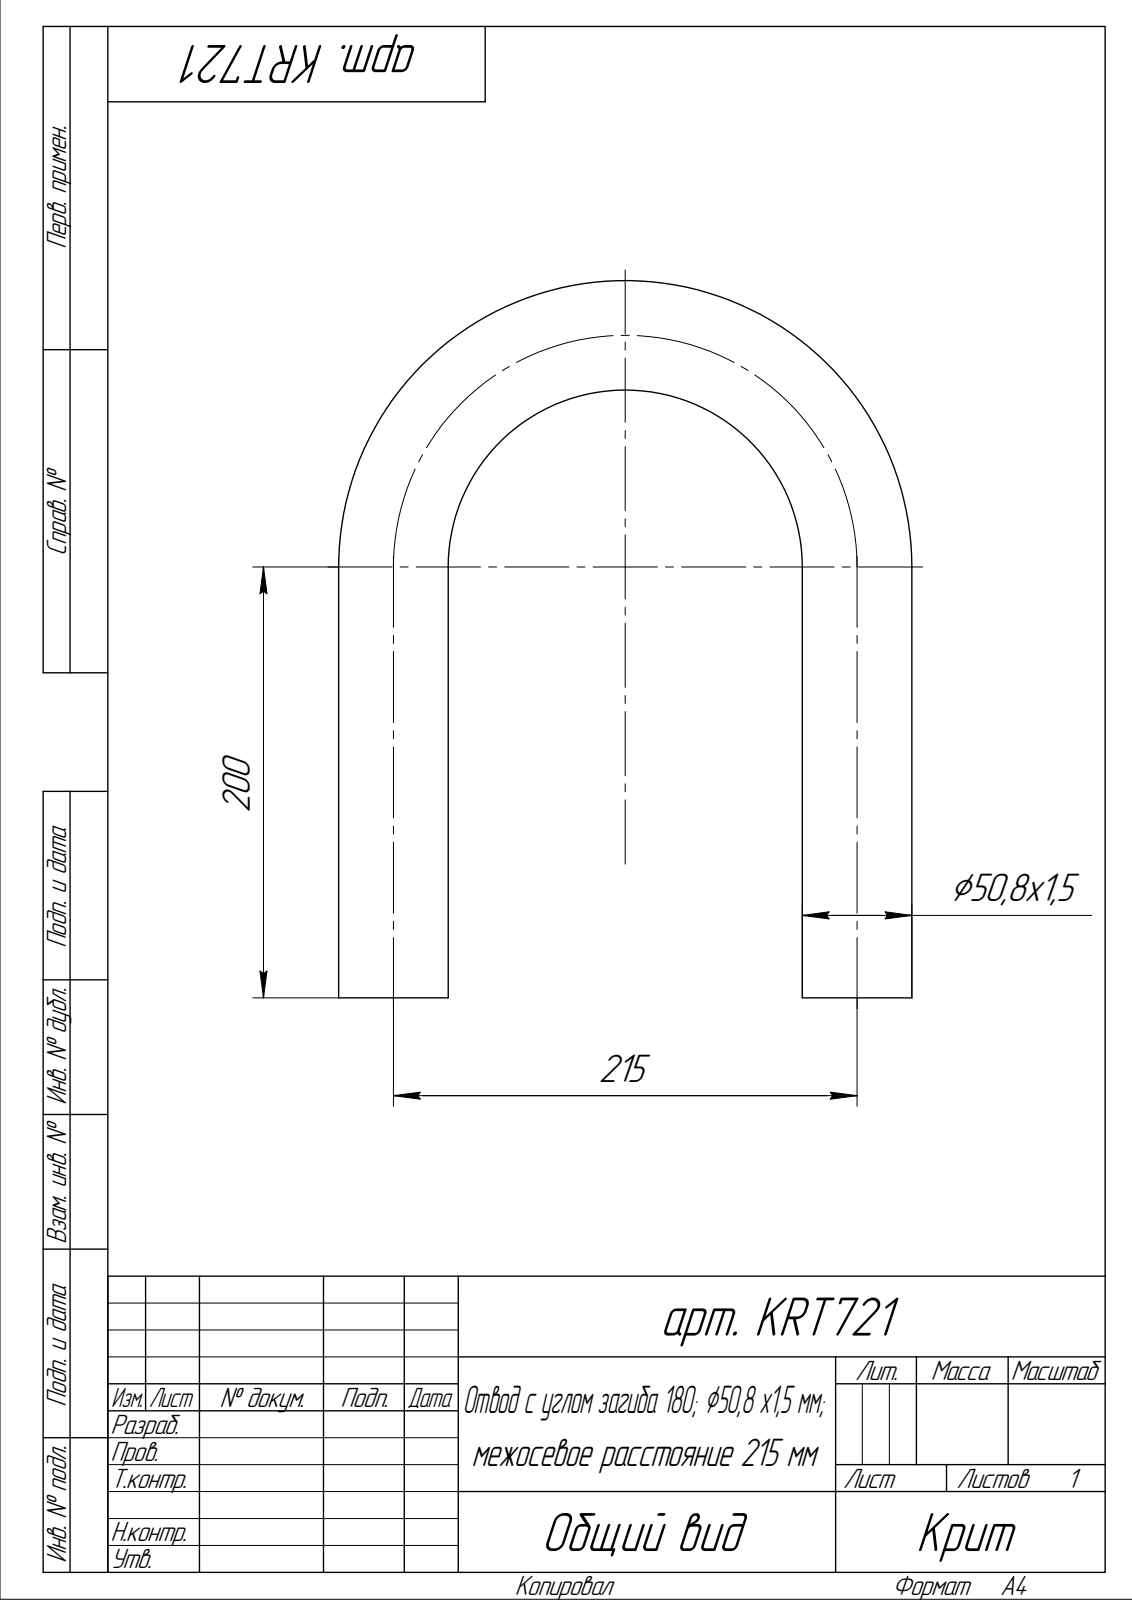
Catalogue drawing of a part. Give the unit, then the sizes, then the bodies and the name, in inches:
Units: inches
Overall size (bounding box): 13.106 × 10.465 × 2
Round holes (diameter × count): ⌀1.882 ×2
Round bosses / shafts (diameter × count): ⌀2 ×2
Hole centre spacings: 8.465
Volume: 10.46 in³ · Surface area: 354.9 in²
Bodies: 1 solid, 8 faces (2 planar, 4 cylindrical, 2 other)
Part name (STEP PRODUCT): Деталь
STEP written by: ASCON Math Kernel (AUTOMOTIVE_DESIGN)
